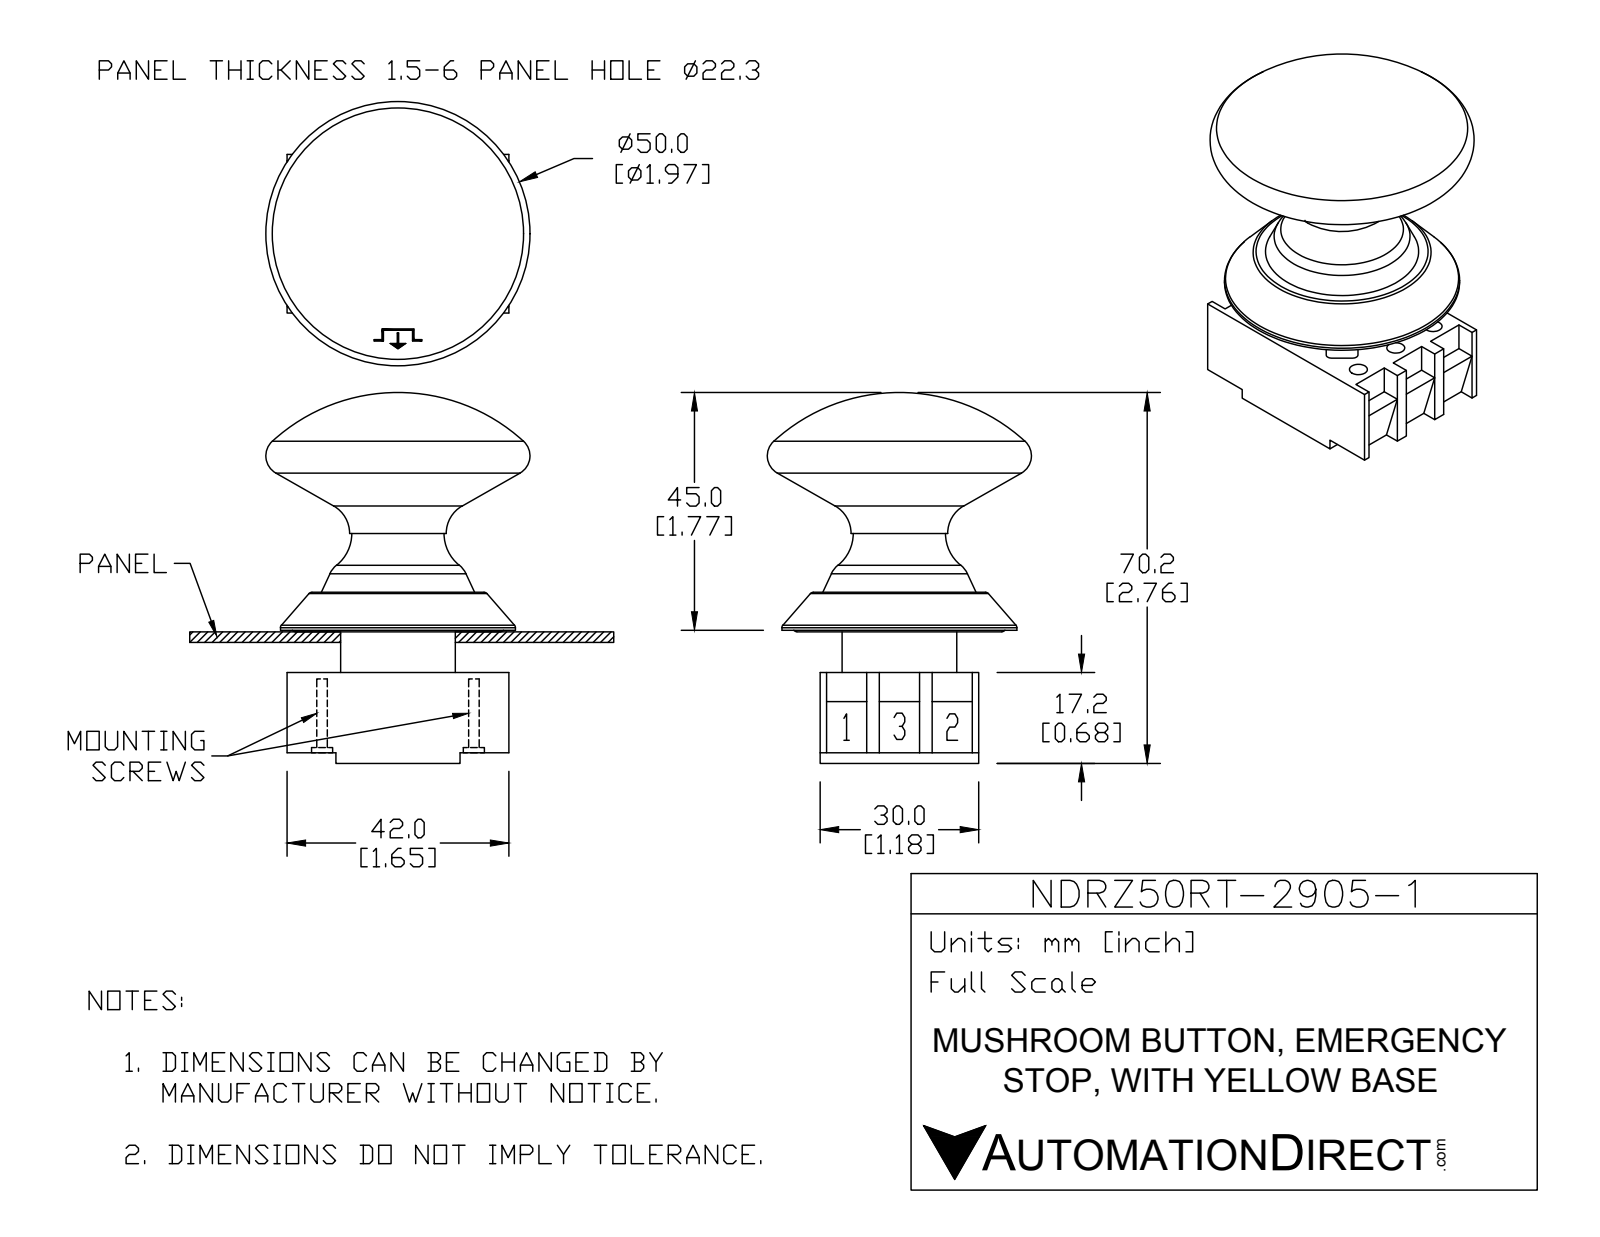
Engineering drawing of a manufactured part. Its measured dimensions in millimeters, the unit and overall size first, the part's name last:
Units: millimetres
Overall size (bounding box): 70.2 × 50 × 50
Round holes (diameter × count): ⌀3.4 ×6, ⌀5 ×6, ⌀12.5 ×1
Round bosses / shafts (diameter × count): ⌀4.6 ×2, ⌀4 ×2, ⌀44.5 ×1, ⌀21.7 ×1
Partial cylindrical surfaces — rounded edges, fillets, slot ends (radius × count): R1 ×8, R8.7 ×5, R11 ×1
Main face-to-face distances: 7.2, 15.2, 30, 8, 7.5, 7.7, 22.9, 10, 23.2, 30.4
Hole centre spacings: 10, 17.52, 30.45, 28.76, 14.38, 20, 35.03
Volume: 55 695 mm³ · Surface area: 21 605 mm²
Bodies: 7 solids, 222 faces (126 planar, 63 cylindrical, 33 other)
Part name (STEP PRODUCT): NDRZ50RT-2905-1
STEP written by: SolidWorks 2016 (AUTOMOTIVE_DESIGN)
